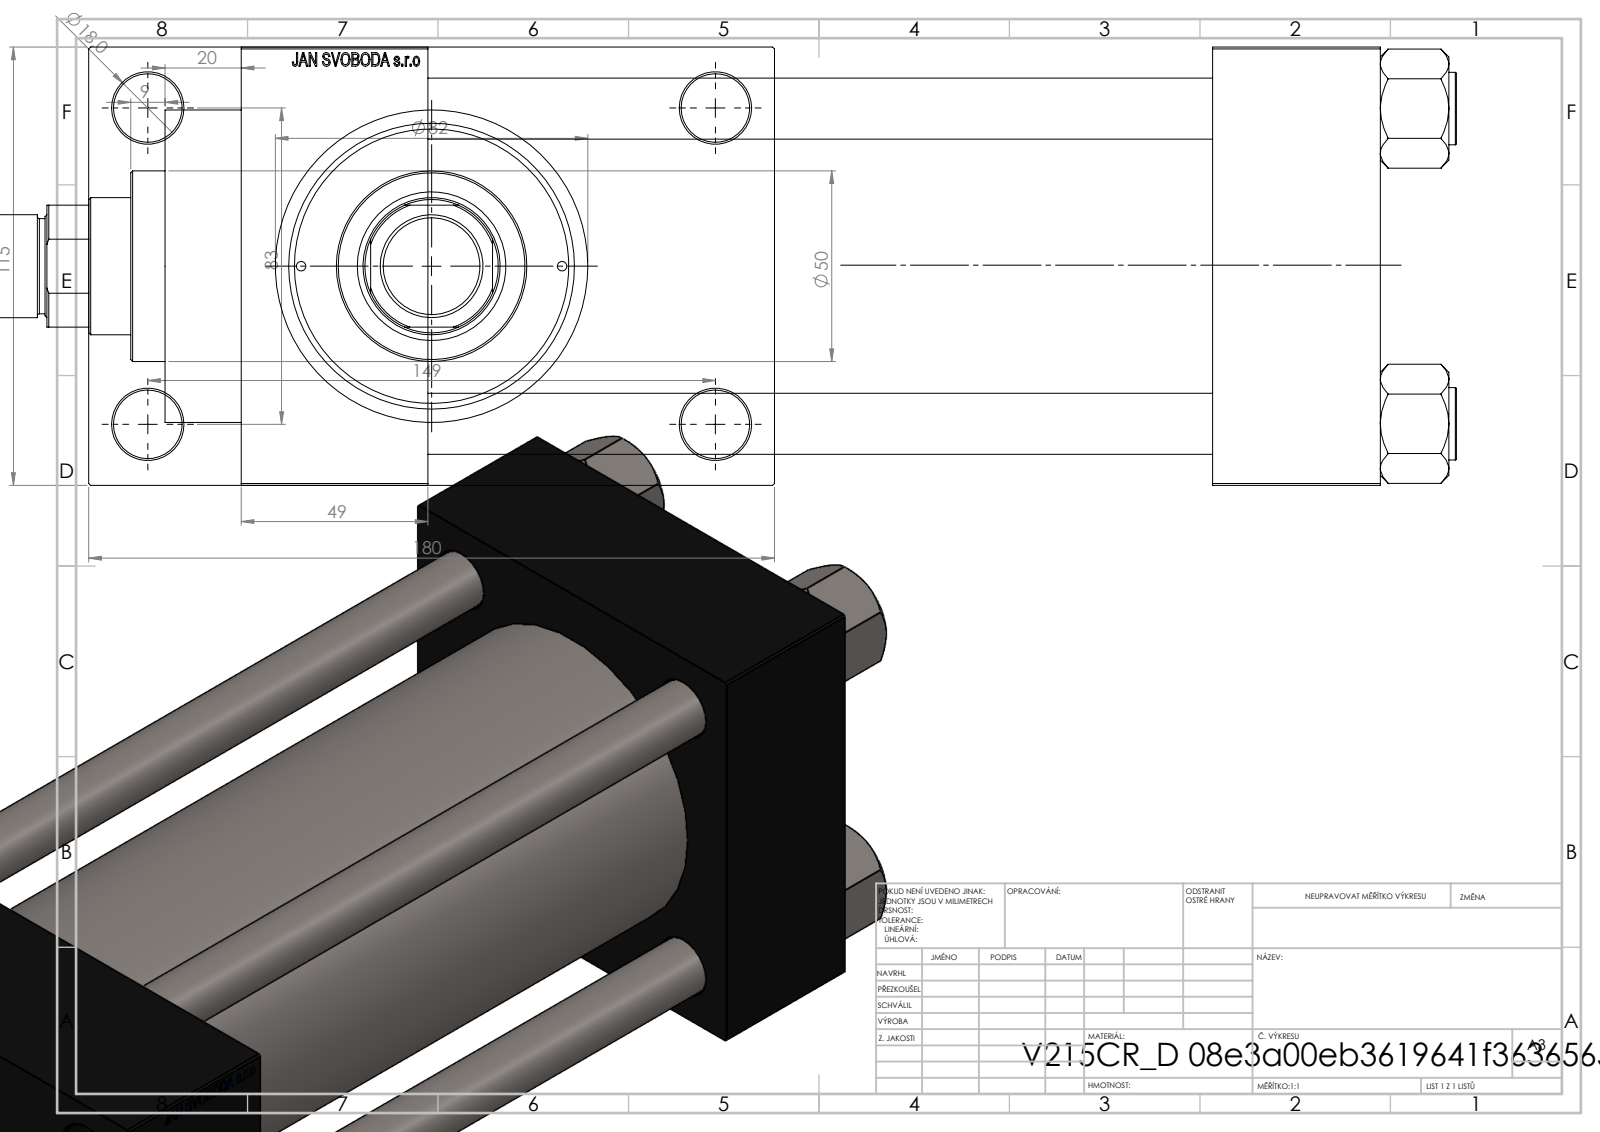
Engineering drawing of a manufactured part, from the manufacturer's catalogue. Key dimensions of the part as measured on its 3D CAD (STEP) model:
Part name (STEP PRODUCT): V215CR_D_Body; V215CR_VCP_D; V215CR_D_TYCINKA; ROD_END_AH (+2 more)
STEP written by: SolidWorks 2019 (CONFIG_CONTROL_DESIGN)
Units: millimetres
Bodies: 12 solids, 1173 faces (551 planar, 96 cylindrical, 526 other)
Overall size (bounding box): 406 × 180 × 115
Volume: 2 364 000 mm³ · Surface area: 417 737 mm²
Round holes (diameter × count): ⌀16 ×4, ⌀18 ×4, ⌀2.5 ×2, ⌀7 ×2, ⌀26.44 ×2, ⌀35 ×2, ⌀25.5 ×1, ⌀36 ×1, ⌀39 ×1, ⌀61 ×1, ⌀72 ×1, ⌀80 ×1
Round bosses / shafts (diameter × count): ⌀19 ×4, ⌀86 ×1, ⌀82 ×1, ⌀50 ×1, ⌀27 ×1, ⌀25 ×1
Partial cylindrical surfaces — rounded edges, fillets, slot ends (radius × count): R17.5 ×1
Main face-to-face distances: 115, 206, 255, 49, 44, 250, 299, 32.5, 147.5, 180
Hole centre spacings: 33.15, 41.96, 57.81, 58.48, 82.7, 85.28, 86.17, 89.24
